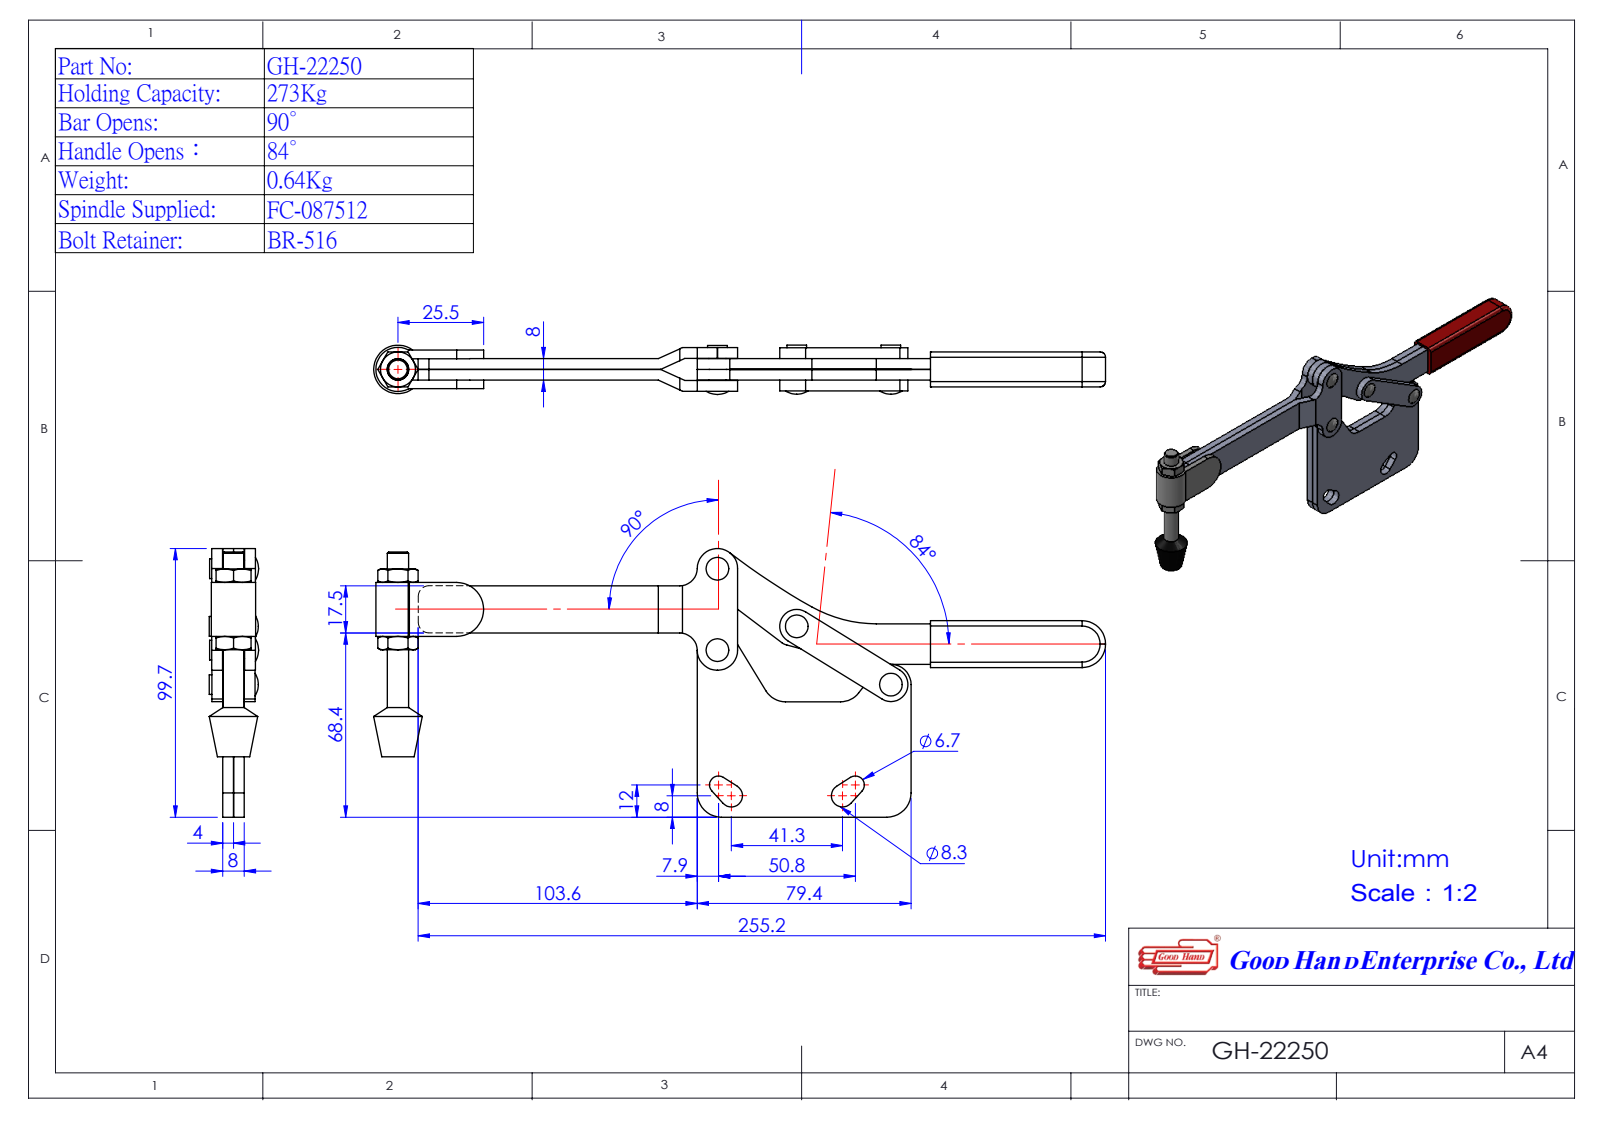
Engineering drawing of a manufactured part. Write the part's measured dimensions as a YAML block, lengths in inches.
part_name: "GH-22250(簡化); Group4^GH-22240(簡化); Group3^GH-22245(簡化); Group5^組合件5 (+2 more)"
step_written_by: "SolidWorks 2016 (AUTOMOTIVE_DESIGN)"
units: inches
bodies: {solids: 5, faces: 237, planar: 96, cylindrical: 105, other: 36}
overall_size: [10.64, 3.925, 0.748]
volume: 5.783
surface_area: 65.84
round_holes:
  - {diameter: 0.197, count: 4}
round_bosses_or_shafts:
  - {diameter: 0.287, count: 4}
  - {diameter: 0.591, count: 1}
  - {diameter: 0.315, count: 1}
partial_cylinders:
  - {radius: 0.039, count: 4}
  - {radius: 0.197, count: 3}
  - {radius: 0.132, count: 2}
  - {radius: 0.157, count: 2}
  - {radius: 0.163, count: 2}
  - {radius: 0.248, count: 2}
  - {radius: 0.256, count: 2}
  - {radius: 0.295, count: 2}
face_to_face_distances: [0.315, 0.157, 0.161, 0.319, 0.098, 0.476, 0.256, 0.413, 0.512, 0.094]
hole_center_spacings: [1.189, 1.21, 1.433, 1.618, 2.585, 3.049]
